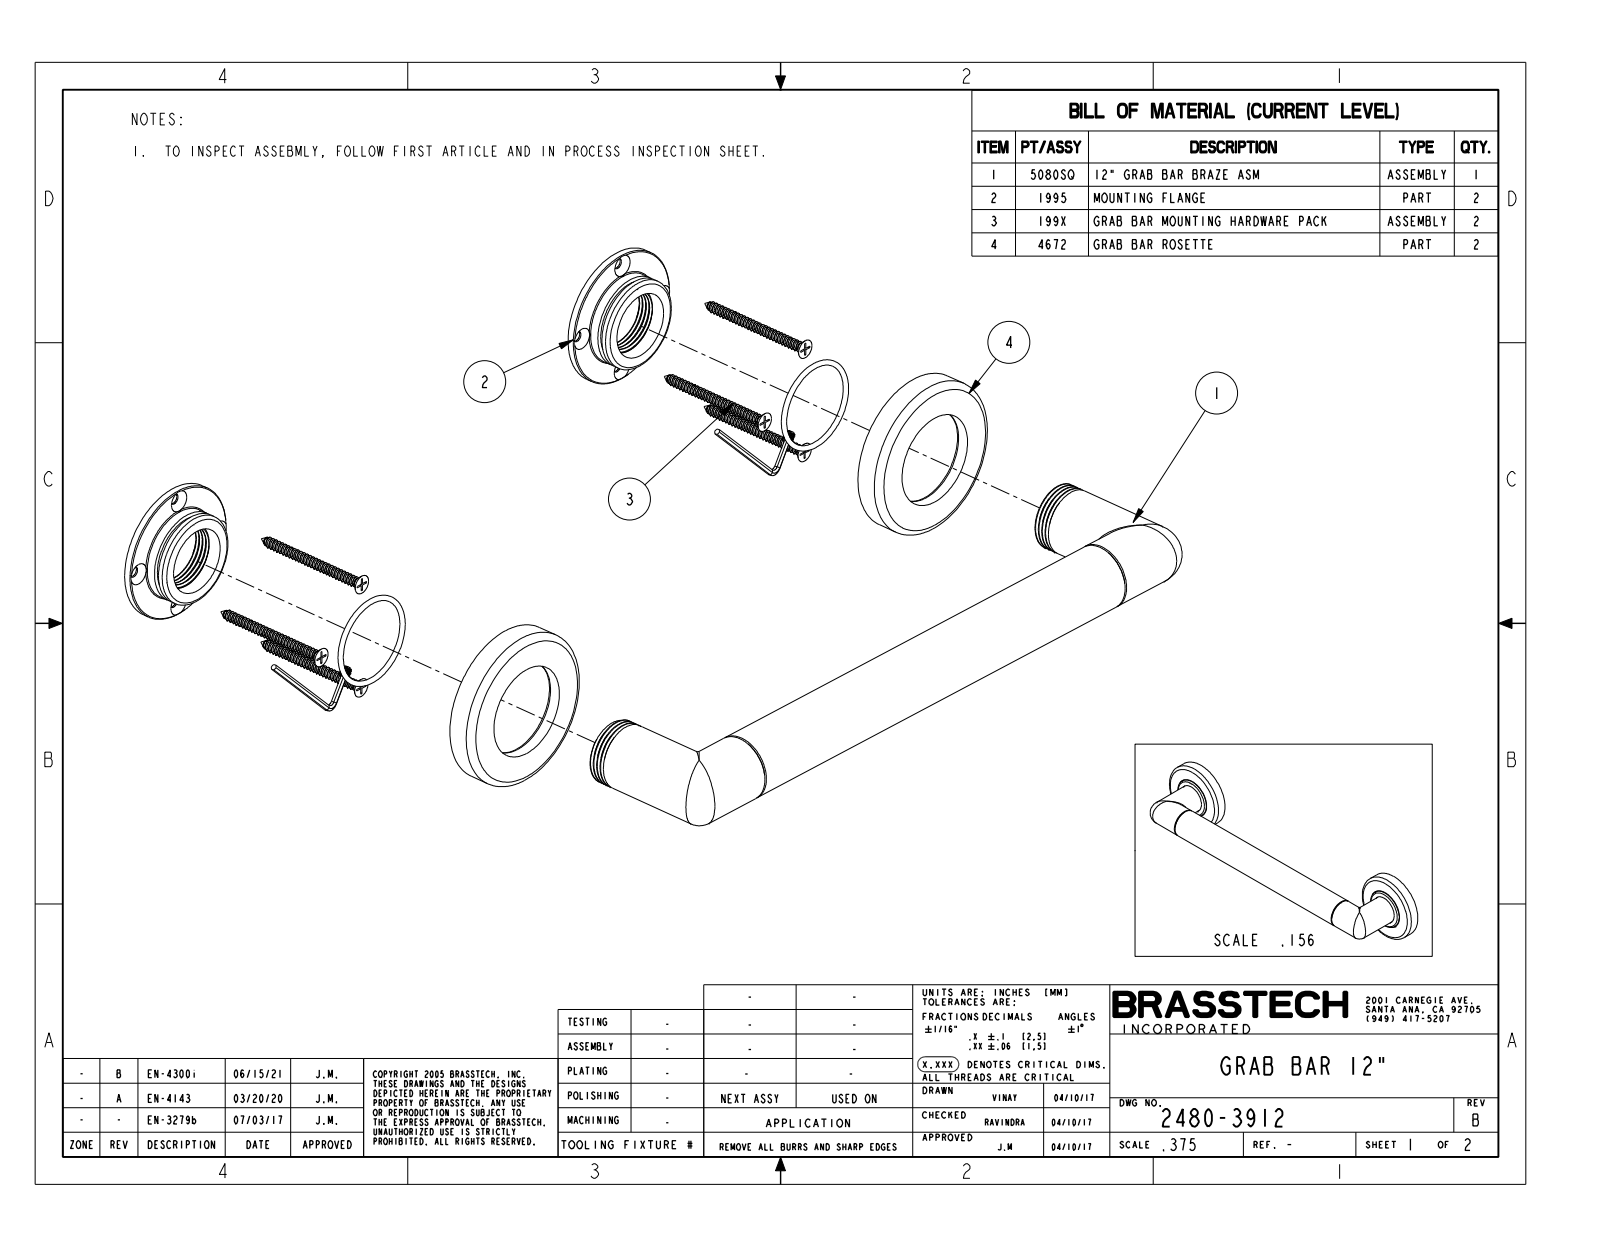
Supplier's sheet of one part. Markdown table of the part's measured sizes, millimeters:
| quantity | value |
| --- | --- |
| part name | 2480-3912 |
| STEP written by | CREO PARAMETRIC BY PTC INC, 2018400 (AUTOMOTIVE_DESIGN) |
| units | millimeters |
| bodies | 1 solid, 48 faces (6 planar, 18 cylindrical, 24 other) |
| overall size | 381 × 76.2 × 70 |
| volume | 429 200 mm³ |
| surface area | 60 740 mm² |
| round bosses / shafts (diameter × count) | 31.8 × 3, 76.2 × 2, 44.5 × 2 |
| main face-to-face distances | 13.5, 15.2, 1.8 |
